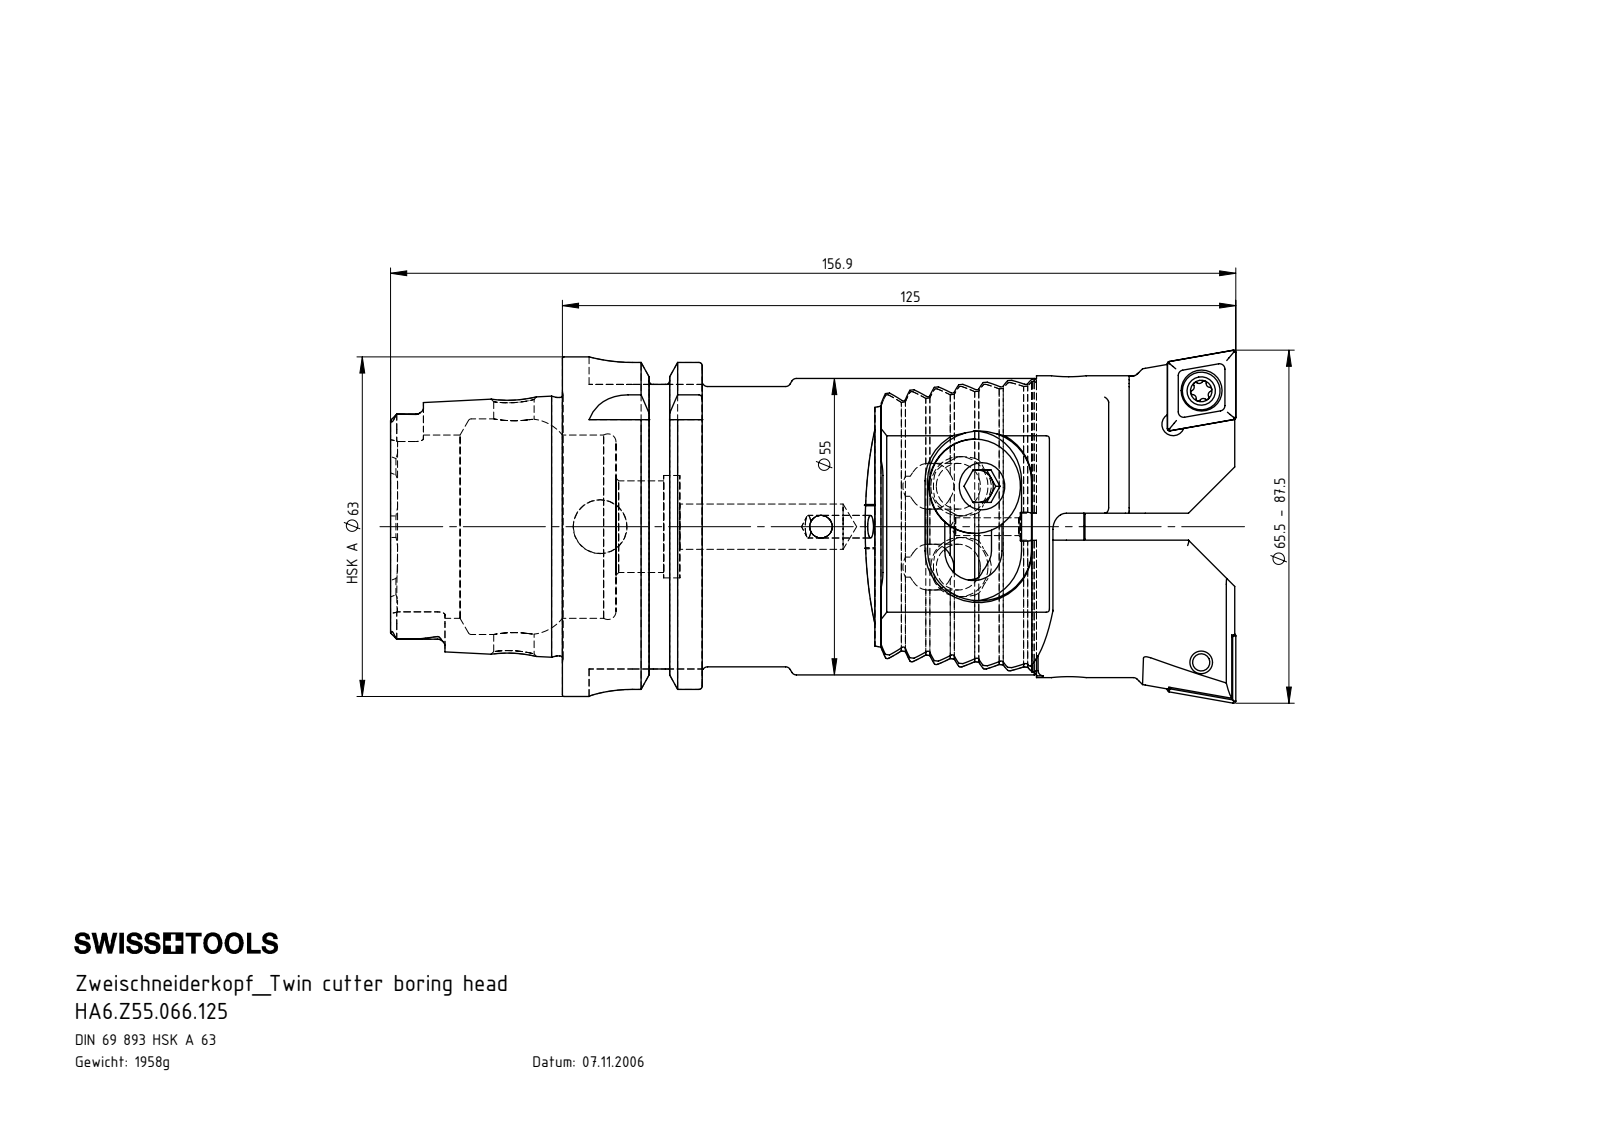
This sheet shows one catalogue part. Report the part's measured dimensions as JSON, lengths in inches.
{"part_name": "Z42-ER2.001.019_A; Z55-ER1.002.025_A; HA6-Z55.K23.125_A_Fertigbearbeitung; Z55-ER1.003.025_A_gespannt (+2 more)", "step_written_by": "SolidWorks 2017 (AUTOMOTIVE_DESIGN)", "units": "inches", "bodies": {"solids": 6, "faces": 361, "planar": 195, "cylindrical": 85, "other": 81}, "overall_size": [5.075, 2.48, 2.48], "volume_in3": 11.49, "surface_area_in2": 61.88, "round_holes": [[0.165, 3], [0.335, 2], [0.413, 2], [0.433, 2], [0.118, 1], [0.13, 1], [0.295, 1], [0.331, 1], [0.394, 1], [0.669, 1], [0.748, 1], [1.339, 1]], "round_bosses_or_shafts": [[0.689, 2], [0.669, 2], [0.394, 2], [2.48, 1], [2.165, 1], [2.163, 1], [2.047, 1], [1.887, 1]], "partial_cylinders_radius": [[0.013, 14], [0.055, 6], [0.113, 4], [0.315, 4], [8.661, 2]], "face_to_face_distances": [0.16, 0.32, 0.481, 0.641, 0.801, 1.022, 0.63, 0.392, 3.465, 3.073], "hole_center_spacings": [1.614]}
